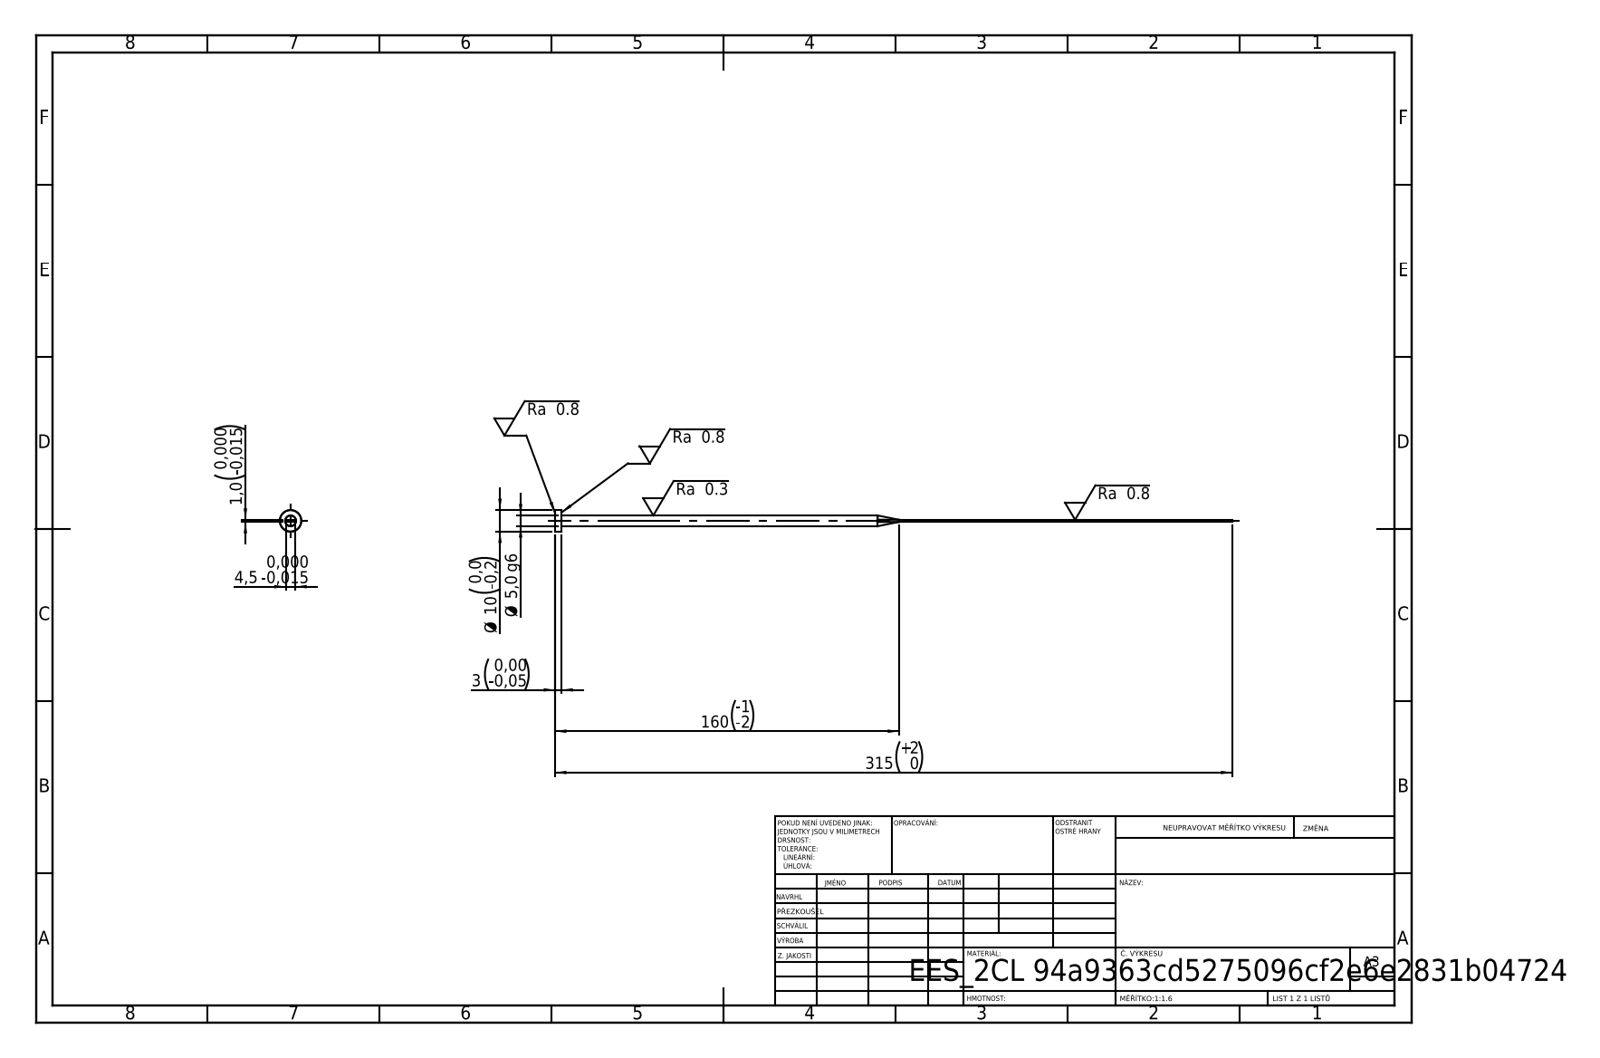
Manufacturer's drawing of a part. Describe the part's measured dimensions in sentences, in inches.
Its 3-D file was written by "SolidWorks 2019 (CONFIG_CONTROL_DESIGN)". It is 1 solid with 15 faces: 7 planar, 4 cylindrical and 4 other. Overall it measures 12.402 by 0.394 by 0.394 inches. Its volume is 0.24 cubic inches and its surface area 6.787 square inches. Round bosses or shafts: 1 of diameter 0.394, 1 of diameter 0.197. The main face-to-face distances are 0.039, 0.177, 0.118, 12.402, 12.283.
